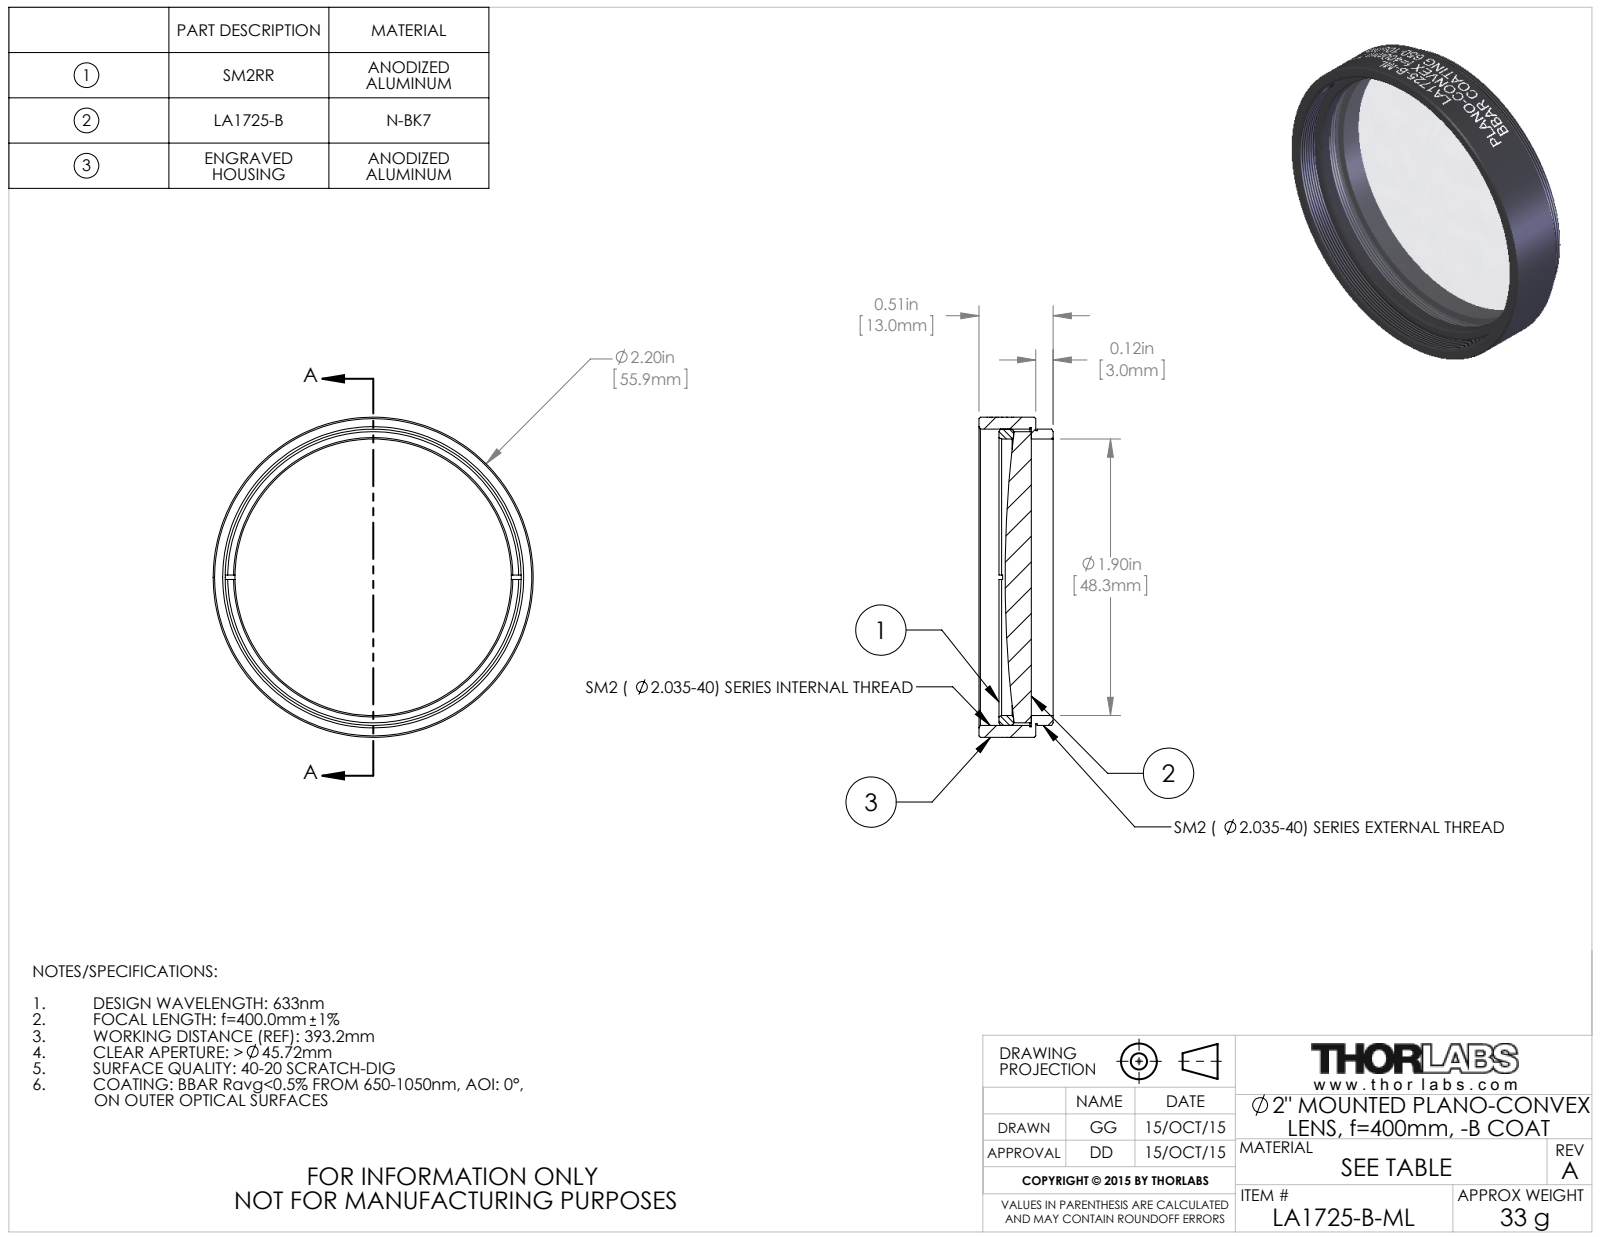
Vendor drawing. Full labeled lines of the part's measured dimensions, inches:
Part name (STEP PRODUCT): TTN039612-E0W
STEP written by: SolidWorks 2014 (CONFIG_CONTROL_DESIGN)
Units: inches
Bodies: 3 solids, 145 faces (16 planar, 109 cylindrical, 20 other)
Overall size (bounding box): 2.2 × 2.2 × 0.51
Volume: 0.781 in³ · Surface area: 17.6 in²
Round holes (diameter × count): ⌀1.9 ×1, ⌀2.055 ×1
Round bosses / shafts (diameter × count): ⌀2.2 ×1, ⌀2.035 ×1, ⌀2.015 ×1, ⌀2 ×1
Main face-to-face distances: 0.03, 0.39, 0.36, 0.12, 0.15, 0.51, 0.272, 0.152, 0.122, 0.238
